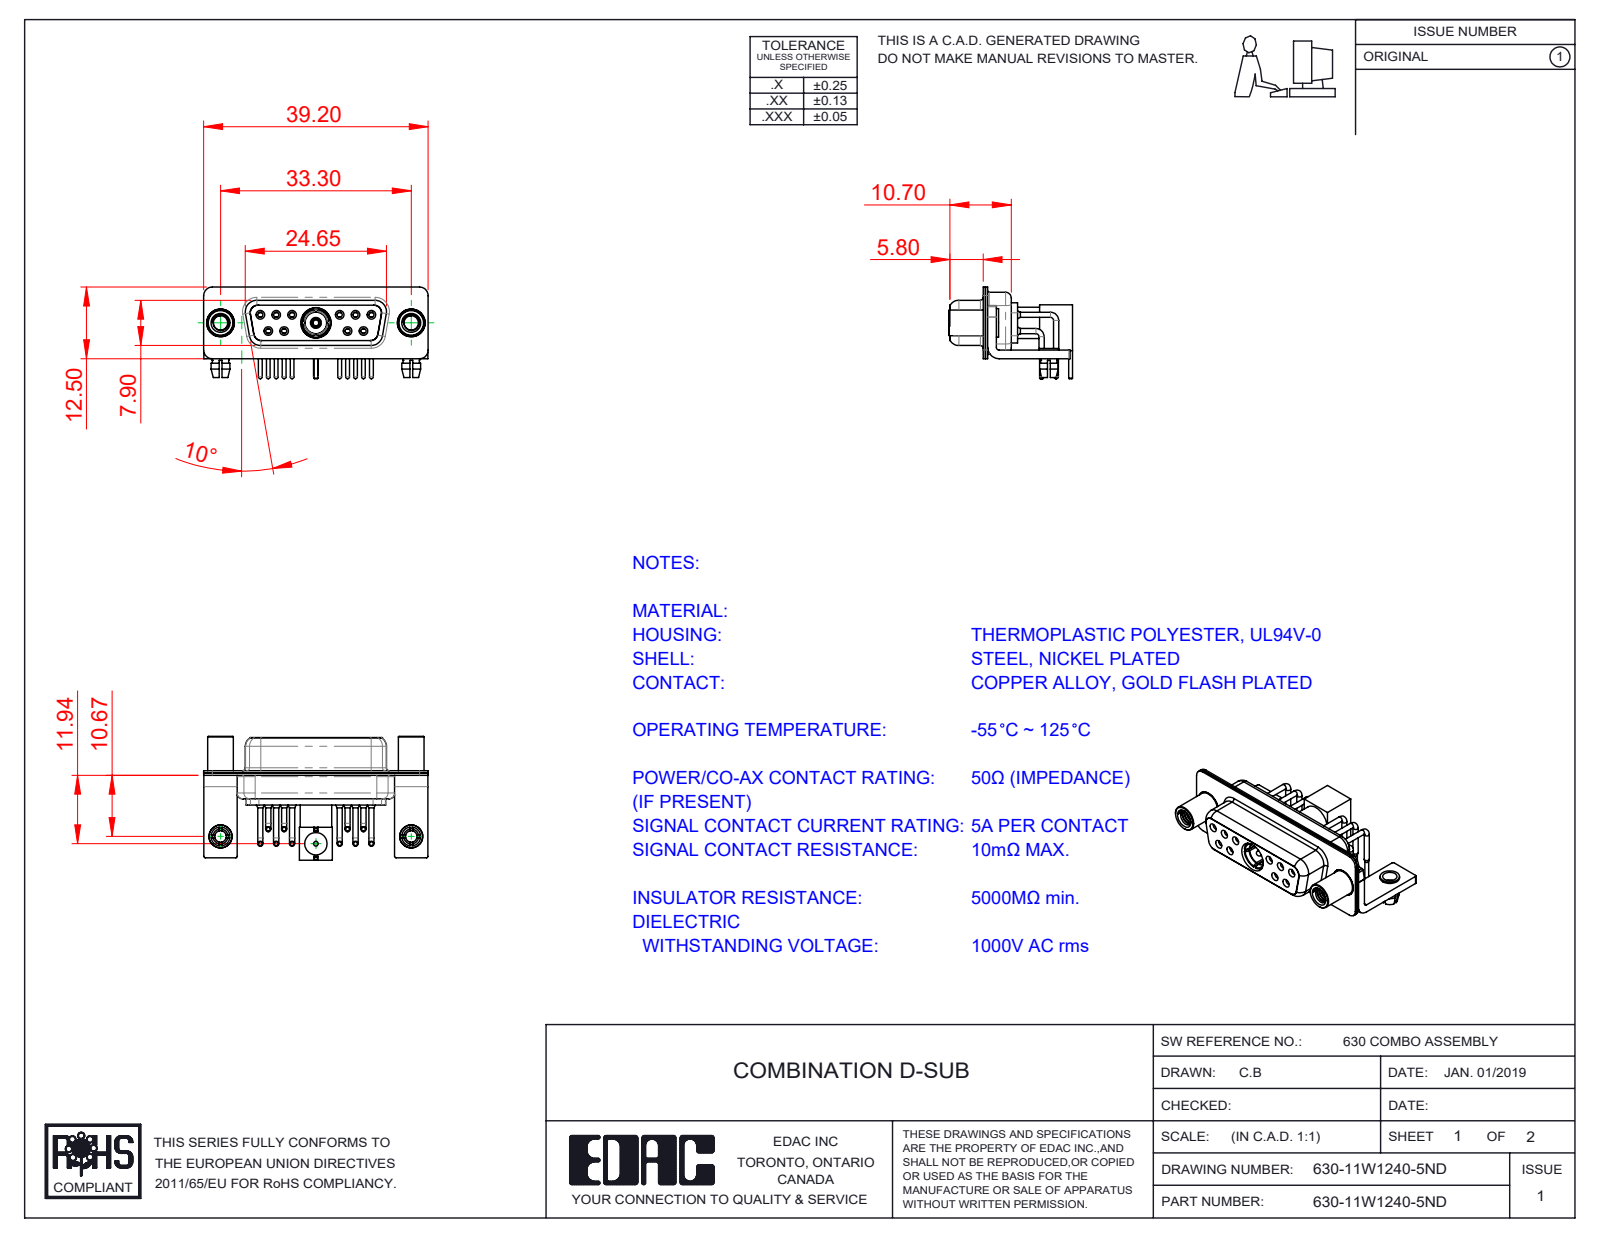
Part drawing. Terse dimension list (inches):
name: Co-Ax Plug Assy_RA; 630Combo Board Lock; 630Combo Shell Front_15 Contacts; 630Combo Housing_11W1 (+8 more)
written by: SolidWorks 2020 (CONFIG_CONTROL_DESIGN)
unit: in
bodies: 25 solids, 1167 faces (354 planar, 536 cylindrical, 277 other)
size: 1.543 × 0.851 × 0.63
volume: 0.197 in³; area: 12.44 in²
holes: 12× ⌀0.079, 11× ⌀0.043, 11× ⌀0.059, 10× ⌀0.035, 6× ⌀0.067, 4× ⌀0.063, 4× ⌀0.098, 3× ⌀0.191, 2× ⌀0.126, 2× ⌀0.157, 2× ⌀0.159, 1× ⌀0.031
bosses: 10× ⌀0.035, 10× ⌀0.026, 6× ⌀0.063, 3× ⌀0.197, 3× ⌀0.157, 3× ⌀0.114, 2× ⌀0.195, 2× ⌀0.189
rounds: 16× R0.01, 16× R0.059, 13× R0.079, 12× R0.053, 8× R0.063, 5× R0.02, 4× R0.024, 4× R0.026
face distances: 0.016, 0.031, 0.055, 0.018, 0.071, 0.333, 0.35, 0.059, 0.244, 0.091
hole spacings: 0.124, 0.109, 0.545, 0.436, 0.654, 0.198, 0.198, 0.218
